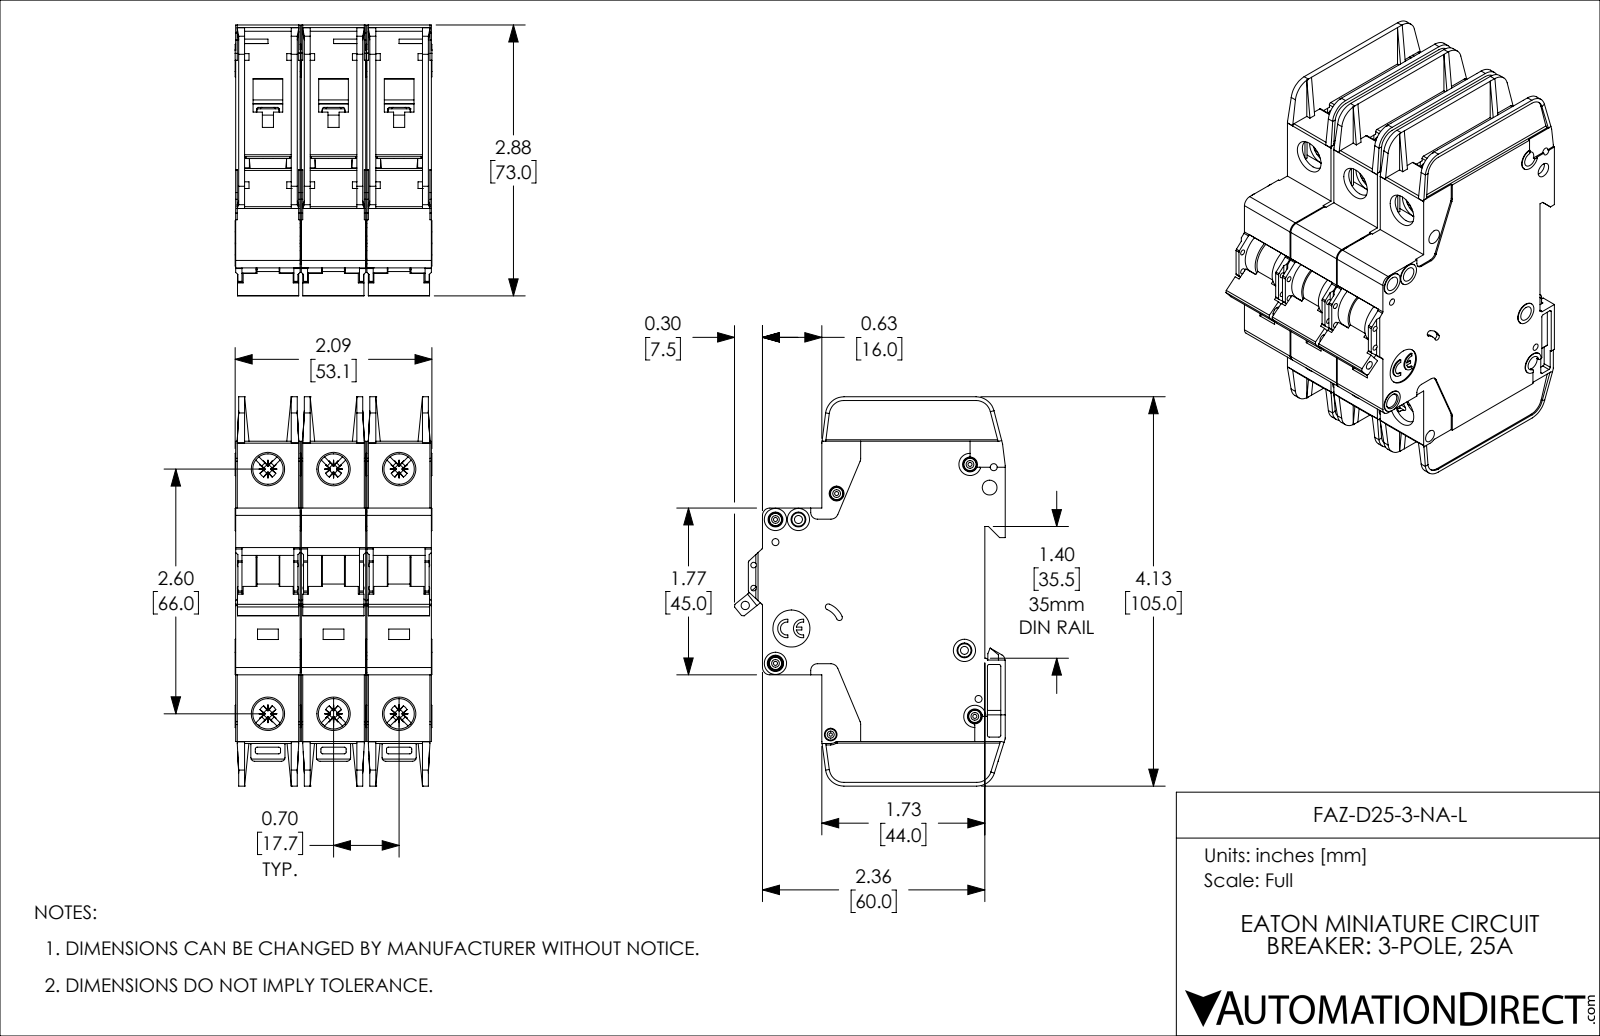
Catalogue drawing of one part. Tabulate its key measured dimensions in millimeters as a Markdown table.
| quantity | value |
| --- | --- |
| part name | FAZ-D25-3-NA-L |
| STEP written by | SolidWorks 2019 (AUTOMOTIVE_DESIGN) |
| units | millimeters |
| bodies | 3 solids, 3381 faces (2013 planar, 1071 cylindrical, 297 other) |
| overall size | 105 × 73.1 × 53.1 |
| volume | 230 200 mm³ |
| surface area | 79 350 mm² |
| round holes (diameter × count) | 4 × 8, 8.2 × 6, 1.1 × 5, 1.9 × 4, 1.5 × 2, 2.2 × 2, 0.9 × 1, 2.3 × 1, 2.5 × 1, 3.4 × 1, 10 × 1 |
| round bosses / shafts (diameter × count) | 3.3 × 5, 6 × 4, 3 × 4, 2.5 × 3 |
| partial cylindrical surfaces (radius × count) | 0.5 × 72, 0.4 × 30, 1 × 18, 1.1 × 12, 2 × 12, 0.2 × 6, 0.3 × 6, 0.7 × 6 |
| main face-to-face distances | 17.7, 1.2, 35.4, 17.4, 15, 35.1, 18.9, 16.5, 2.7, 2.4 |
| hole center spacings | 17.7, 68.3, 66, 6.2, 13.6, 22.1, 35.4, 74.9 |
